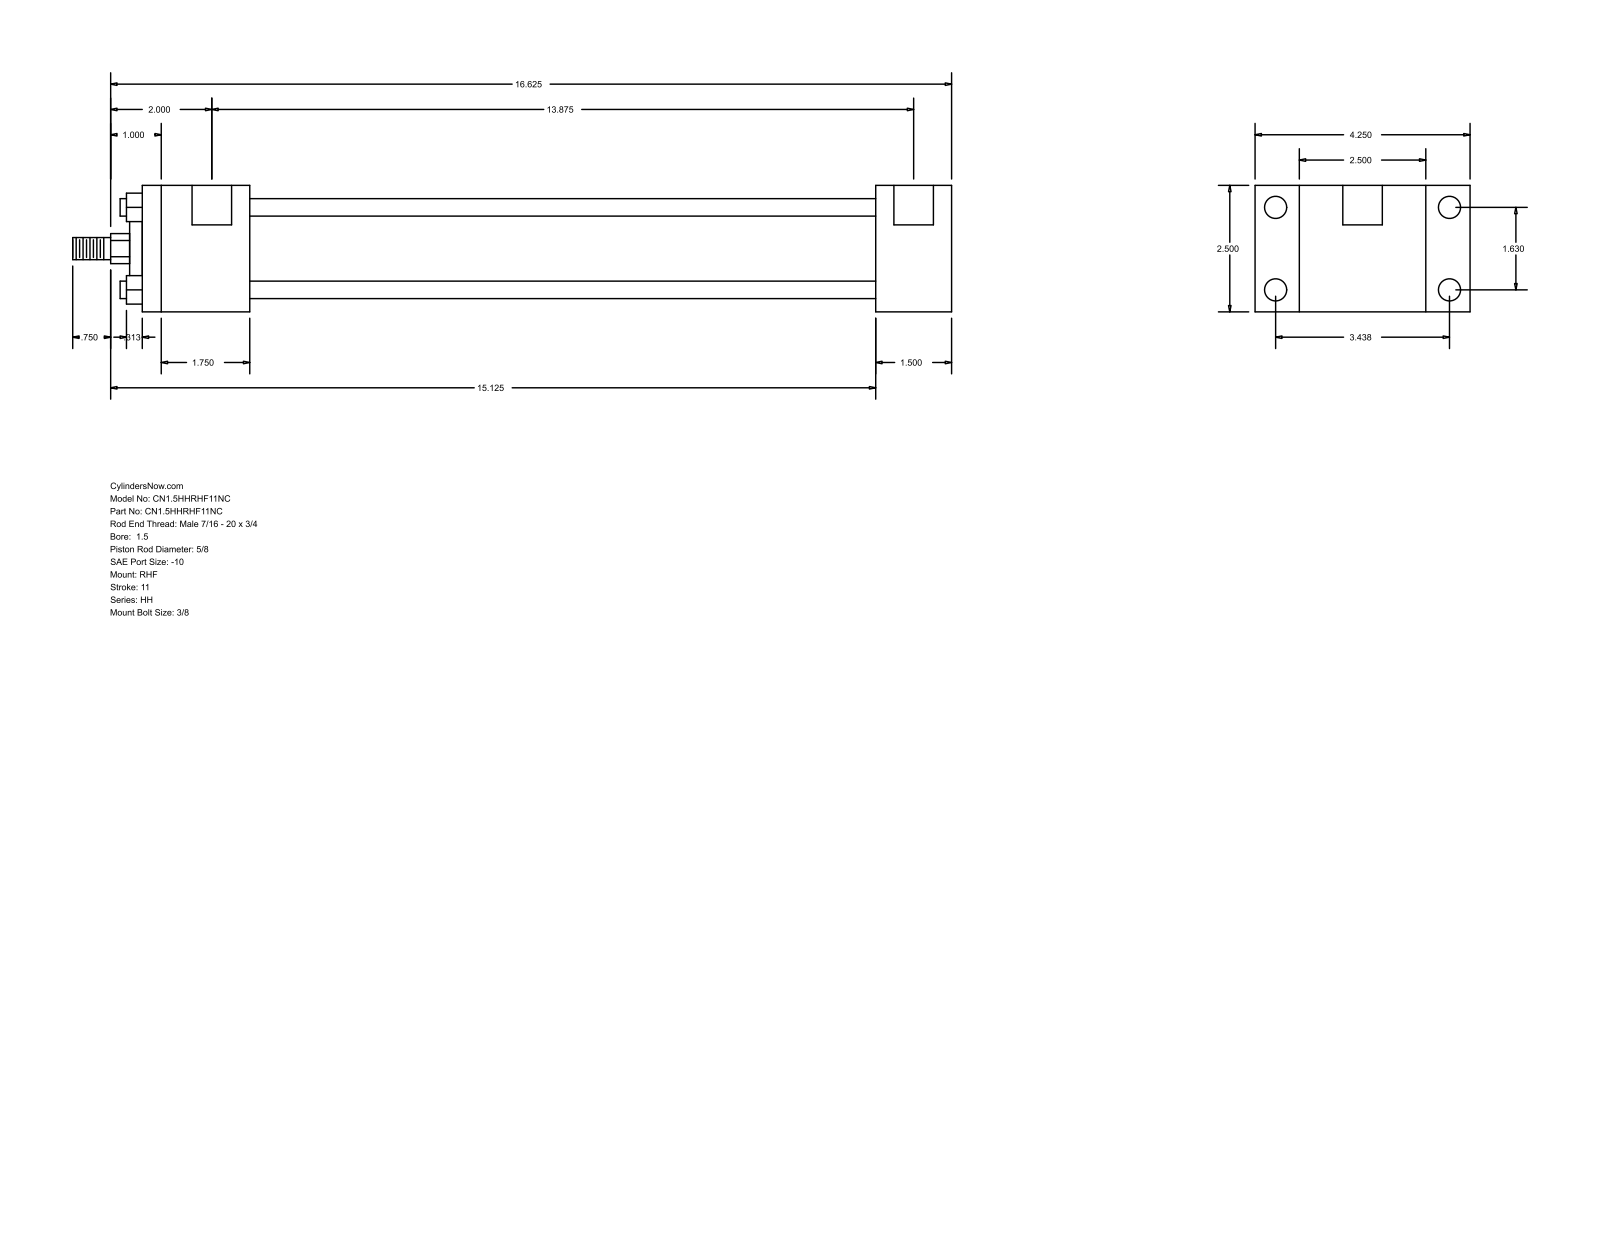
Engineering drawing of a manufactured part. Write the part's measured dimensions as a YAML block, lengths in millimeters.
part_name: "HH_RHF__0150_0.625"
step_written_by: "GSSL Pune (CONFIG_CONTROL_DESIGN)"
units: millimeters
bodies: {solids: 0, faces: 88, planar: 60, cylindrical: 28, other: 0}
overall_size: [441.32, 107.95, 63.5]
round_holes:
  - {diameter: 5.56, count: 4}
  - {diameter: 11.13, count: 4}
  - {diameter: 19.84, count: 2}
round_bosses_or_shafts:
  - {diameter: 8.76, count: 4}
  - {diameter: 44.45, count: 1}
  - {diameter: 28.57, count: 1}
  - {diameter: 15.88, count: 1}
  - {diameter: 11.11, count: 1}
partial_cylinders:
  - {radius: 7.54, count: 1}
face_to_face_distances: [63.5, 22.23, 85.73, 38.09, 368.3, 406.39, 107.96, 53.97, 314.33, 352.42]
hole_center_spacings: [41.4, 87.32, 96.64, 355.6, 1.58, 1.59, 352.43, 354.01]
